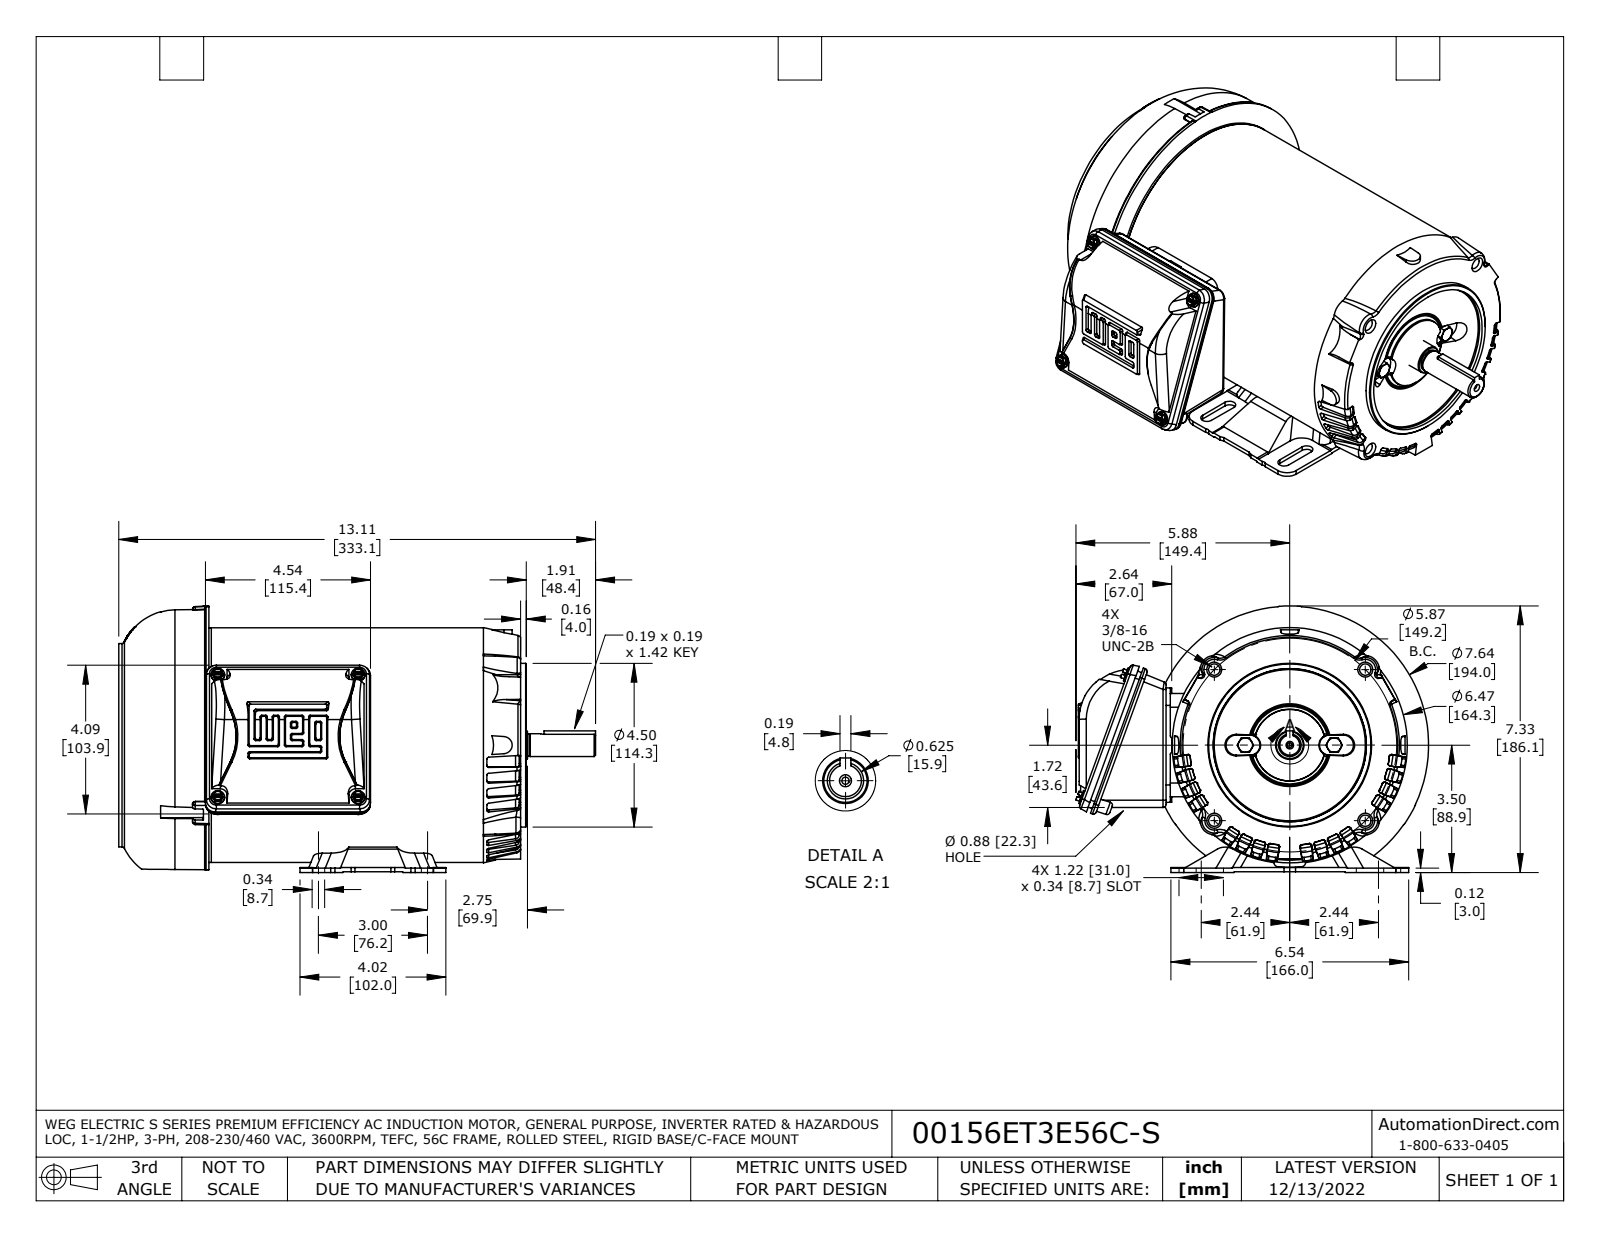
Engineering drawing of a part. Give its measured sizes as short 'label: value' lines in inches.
name: 56C_3PH_TEFC_GP_13109 fxt
written by: SolidWorks 2021 (AUTOMOTIVE_DESIGN)
unit: in
bodies: 13 solids, 1400 faces (539 planar, 331 cylindrical, 530 other)
size: 13.114 × 9.7 × 7.551
volume: 410.3 in³; area: 616.6 in²
holes: 4× ⌀0.313, 1× ⌀0.124
bosses: 4× ⌀0.374, 2× ⌀0.35, 1× ⌀6.447, 1× ⌀6.447, 1× ⌀5.591, 1× ⌀4.5, 1× ⌀0.783, 1× ⌀0.625
rounds: 40× R0.047, 38× R0.006, 32× R0.051, 12× R0.059, 12× R0.087, 10× R0.02, 10× R0.079, 8× R0.171
face distances: 7.547, 2.283, 9.831, 10.854, 8.571, 1.024, 0.197, 2.48, 10.028, 11.051
hole spacings: 2.937, 4.154, 5.874
